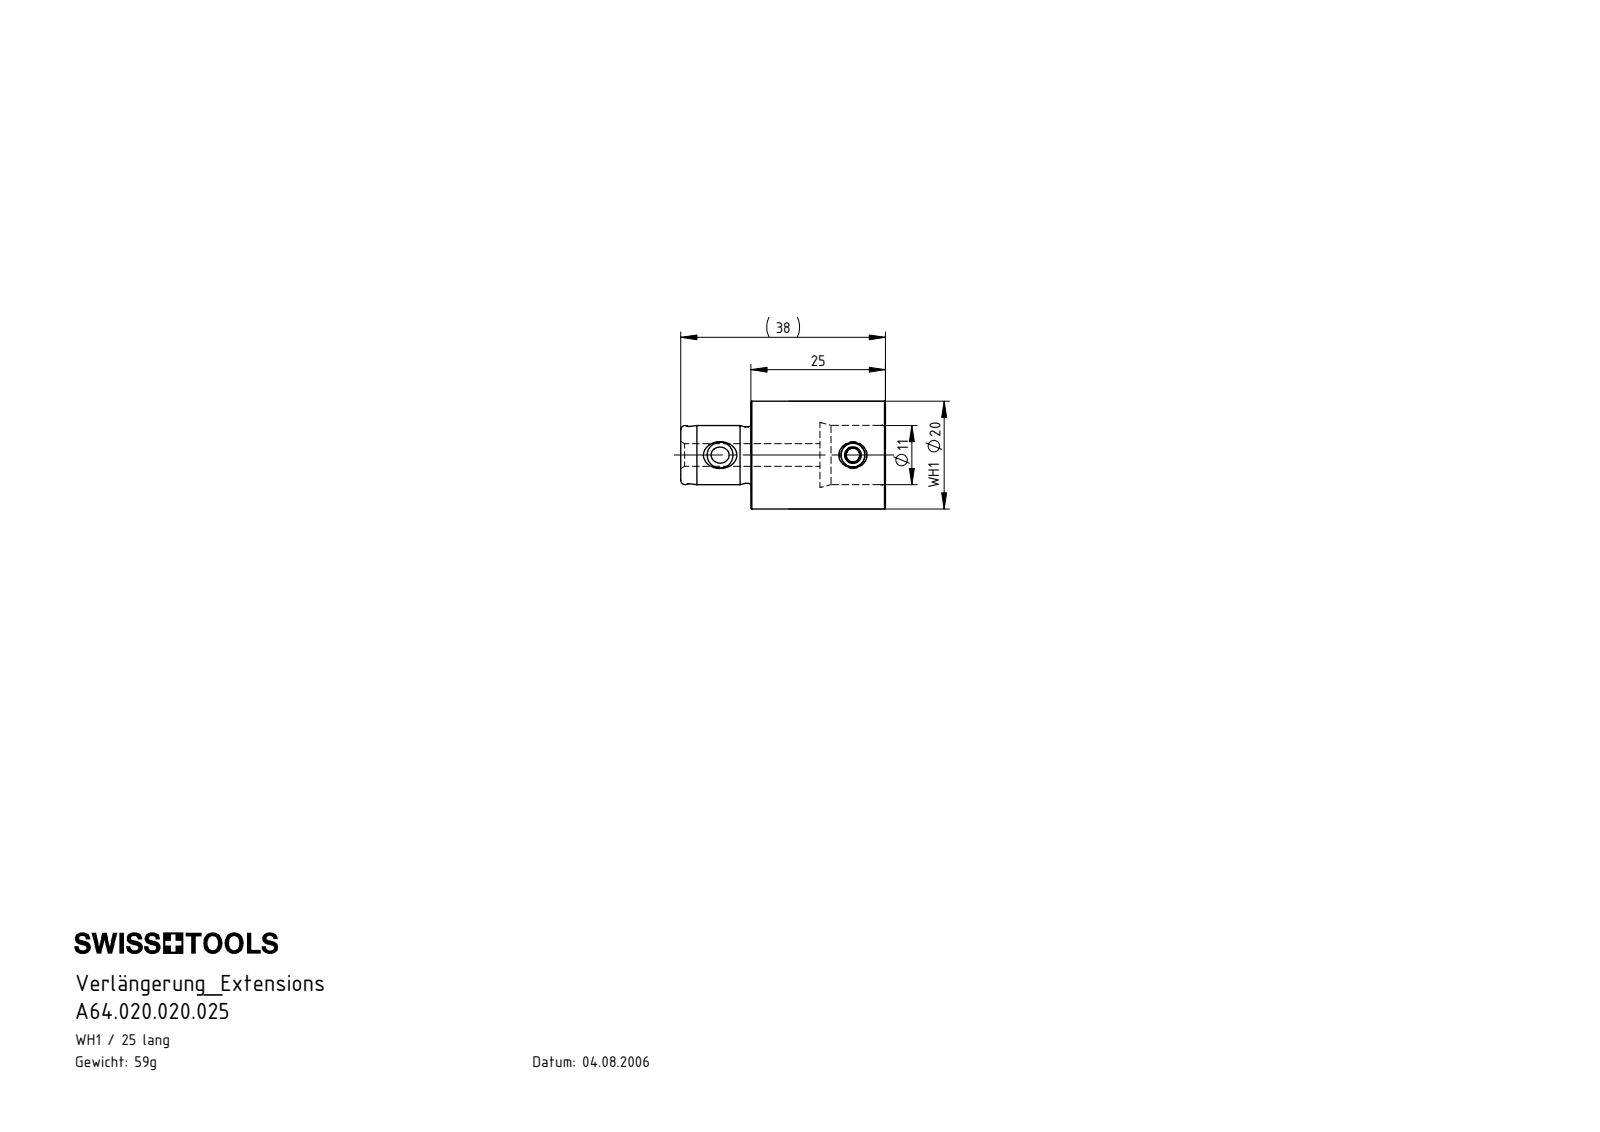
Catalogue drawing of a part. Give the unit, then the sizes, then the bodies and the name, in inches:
Units: inches
Overall size (bounding box): 1.496 × 0.787 × 0.787
Round holes (diameter × count): ⌀0.165 ×1, ⌀0.177 ×1, ⌀0.433 ×1, ⌀0.472 ×1
Round bosses / shafts (diameter × count): ⌀0.787 ×1, ⌀0.413 ×1, ⌀0.197 ×1
Main face-to-face distances: 0.984, 0.504, 0.48, 0.512, 1.016, 1.496, 0.098, 0.295, 0.197
Volume: 0.458 in³ · Surface area: 5.506 in²
Bodies: 2 solids, 69 faces (13 planar, 16 cylindrical, 40 other)
Part name (STEP PRODUCT): WH1-ER1.001.008; WH1-WH1.001.025; WH1-WH1.001.025_A
STEP written by: SolidWorks 2015 (AUTOMOTIVE_DESIGN)
